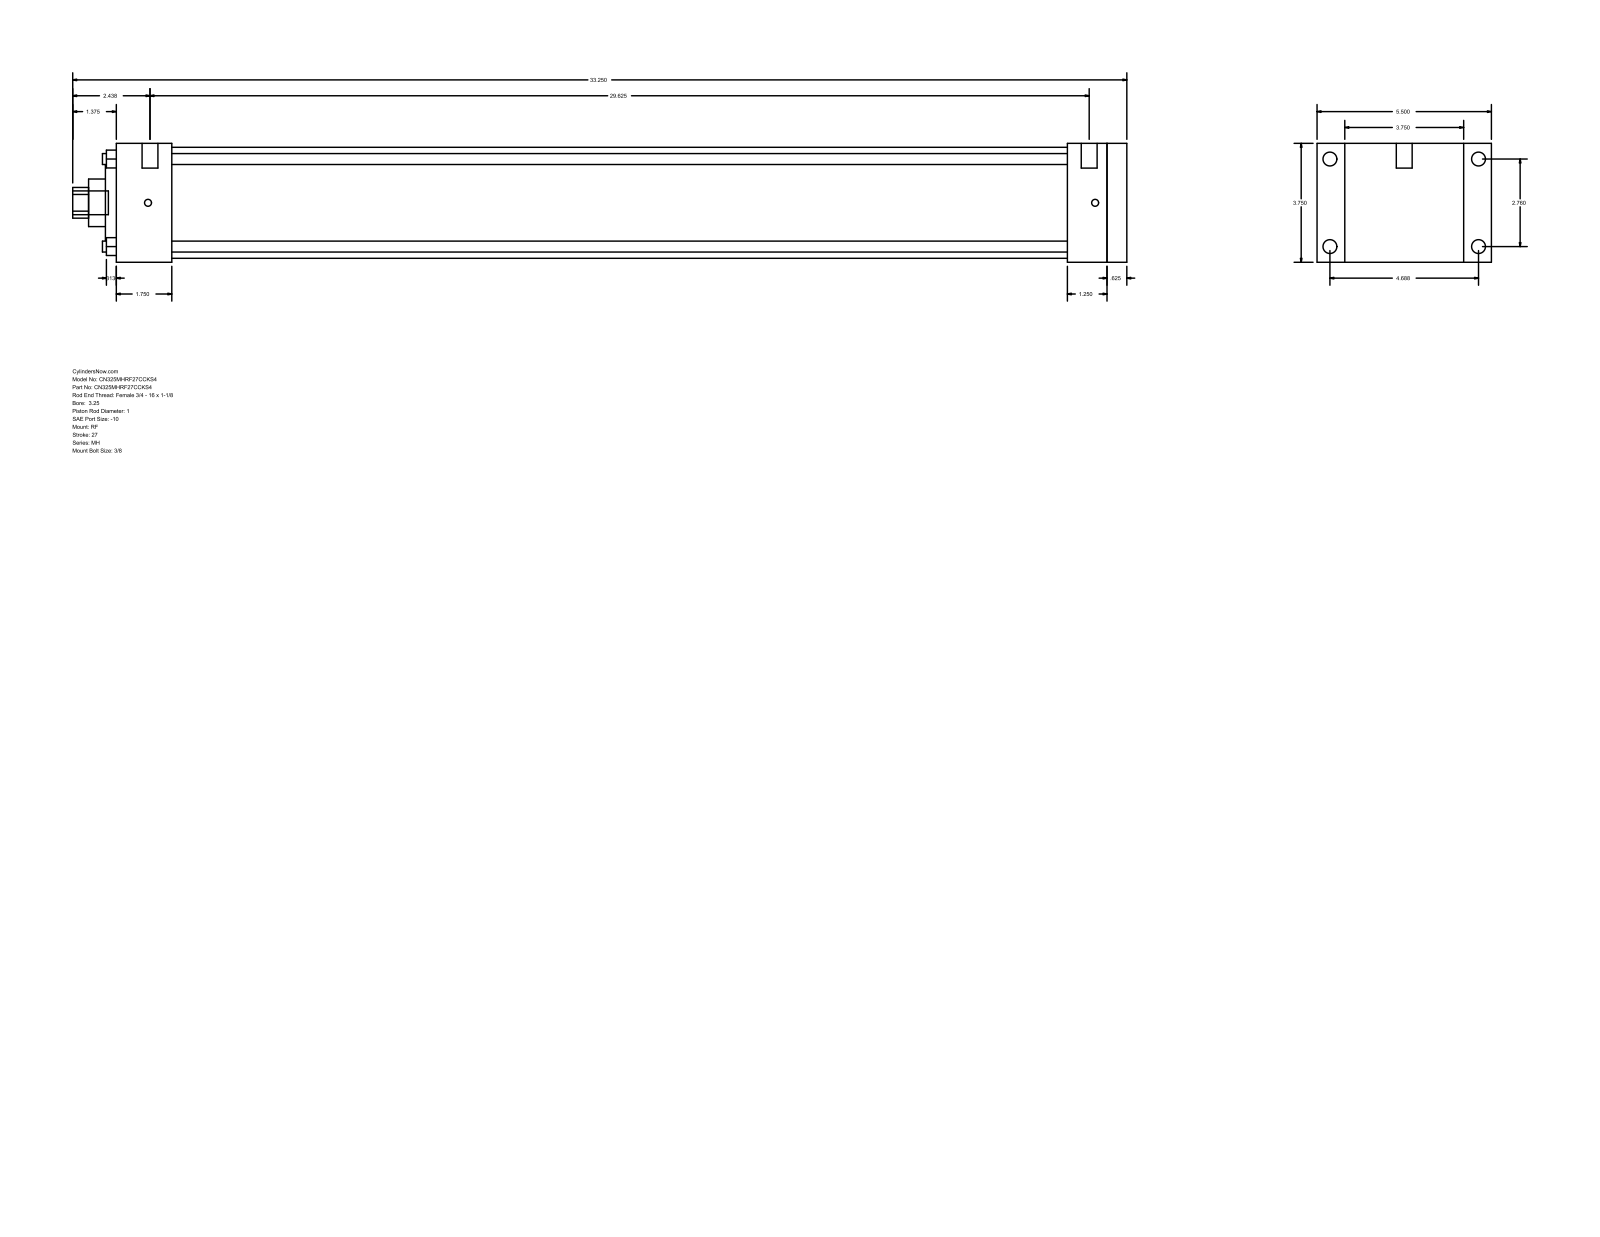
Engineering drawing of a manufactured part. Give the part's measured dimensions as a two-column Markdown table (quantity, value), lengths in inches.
| quantity | value |
| --- | --- |
| part name | MH_RF__0325_1 |
| STEP written by | GSSL Pune (CONFIG_CONTROL_DESIGN) |
| units | inches |
| bodies | 0 solids, 94 faces (65 planar, 29 cylindrical, 0 other) |
| overall size | 33.25 × 5.5 × 3.75 |
| round holes (diameter × count) | 0.345 × 4, 1 × 1, 1.5 × 1, 2.375 × 1, 3.5 × 1 |
| round bosses / shafts (diameter × count) | 0.438 × 4, 0.219 × 4, 0.5 × 2, 0.75 × 1 |
| partial cylindrical surfaces (radius × count) | 0.484 × 1 |
| main face-to-face distances | 3.75, 31.875, 31.25, 0.625, 0.875, 4.625, 1.75, 29.5, 30.125, 30 |
| hole center spacings | 1.952, 2.76, 3.903 |
